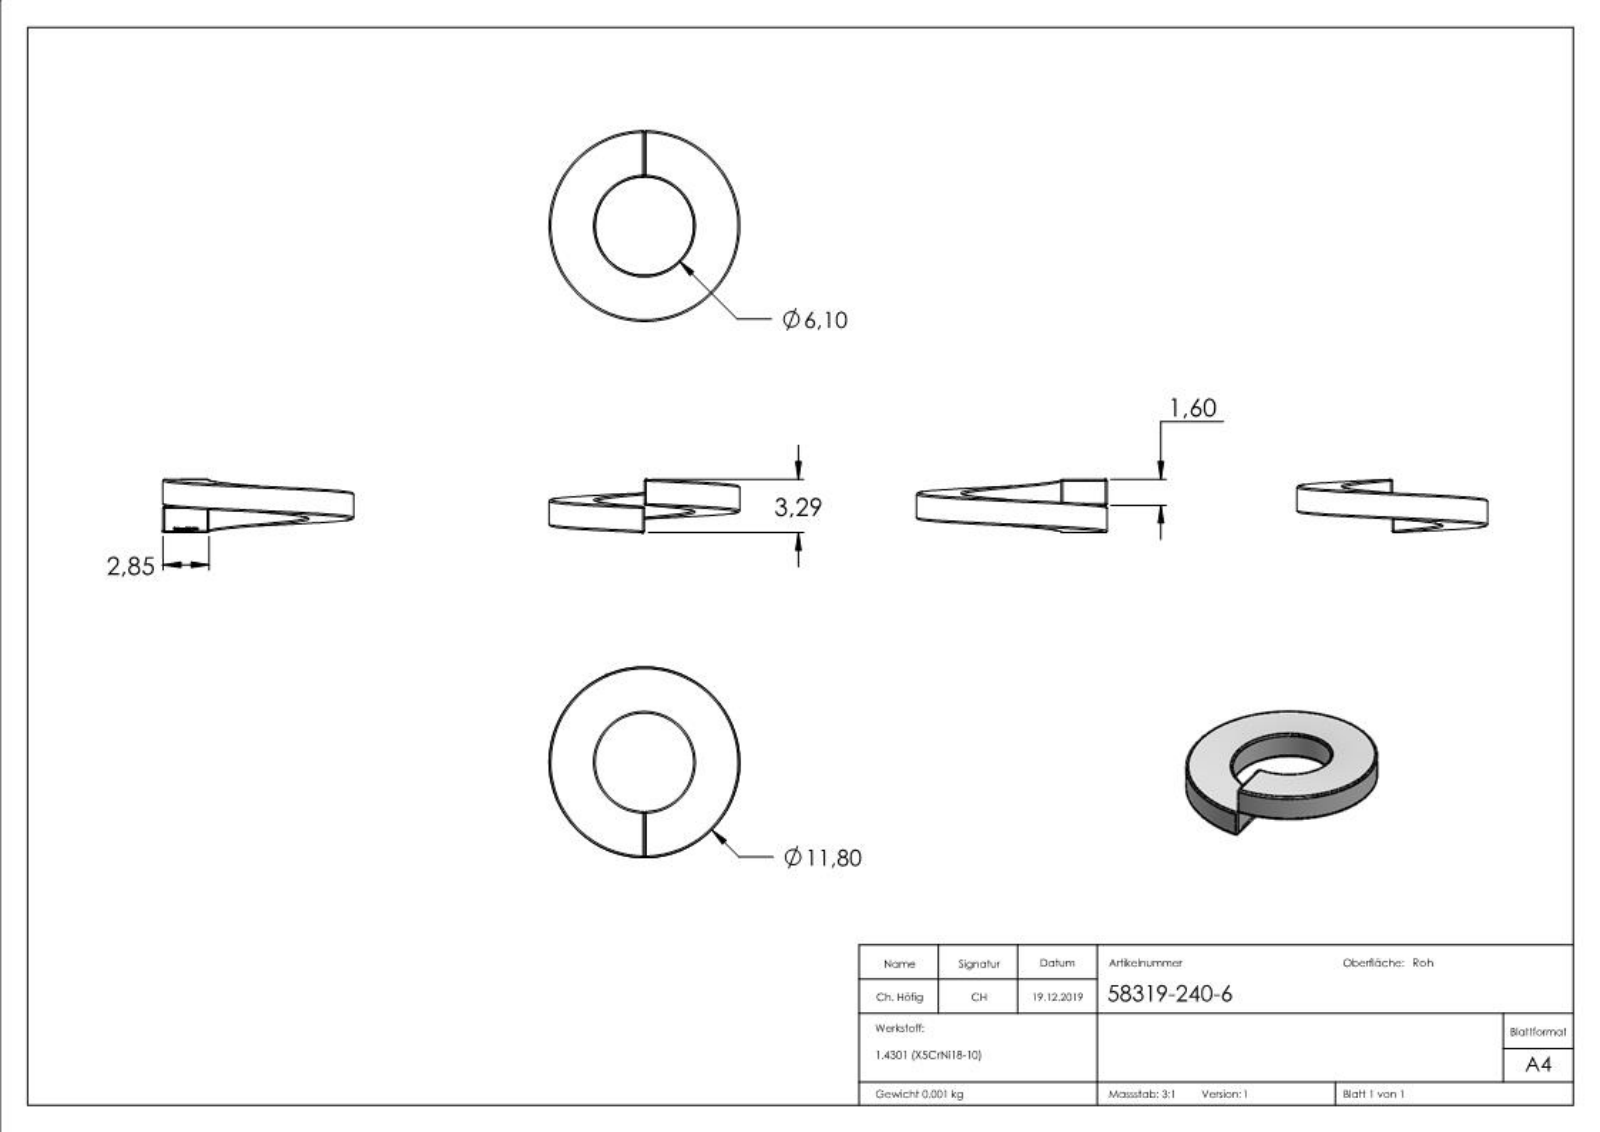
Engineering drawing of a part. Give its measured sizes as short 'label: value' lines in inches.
name: 58319-240-6
written by: SolidWorks 2015 (CONFIG_CONTROL_DESIGN)
unit: in
bodies: 1 solid, 278 faces (132 planar, 0 cylindrical, 146 other)
size: 0.465 × 0.465 × 0.13
volume: 0.008 in³; area: 0.395 in²
face distances: 0.013, 0.019, 0.013, 0.044, 0.023, 0.014, 0.015, 0.02, 0.012, 0.04
